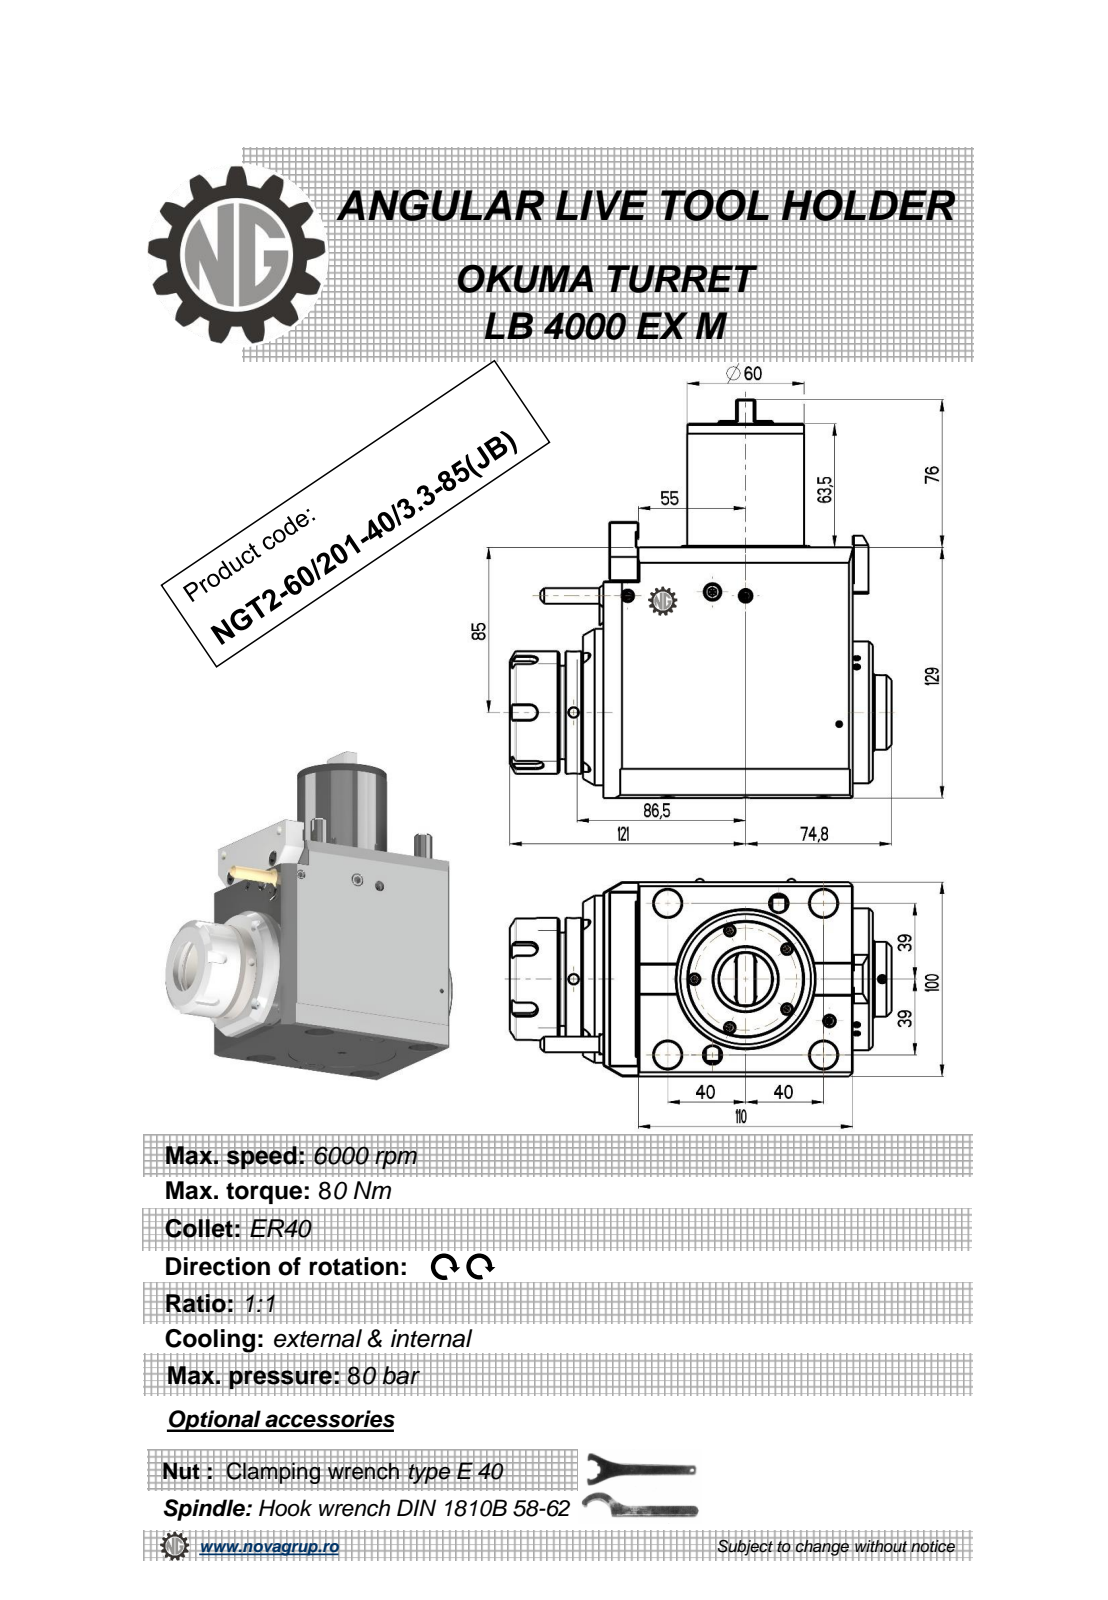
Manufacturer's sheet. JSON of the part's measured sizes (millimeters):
{"part_name": "NGT2_60_201_40_3_3_85_JB", "step_written_by": "PRO/ENGINEER BY PARAMETRIC TECHNOLOGY CORPORATION, 2010280 (CONFIG_CONTROL_DESIGN)", "units": "millimeters", "bodies": {"solids": 2, "faces": 393, "planar": 193, "cylindrical": 91, "other": 109}, "overall_size": [205, 195.8, 100], "volume_mm3": 2054000, "surface_area_mm2": 128659, "round_holes": [[5, 5], [9, 2], [3, 1], [33.5, 1], [71, 1]], "round_bosses_or_shafts": [[12, 4], [6, 3], [86, 1], [73, 1], [63, 1], [60, 1], [51, 1], [38.5, 1]], "partial_cylinders_radius": [[0.31, 10], [0.22, 6], [3.75, 5], [0.8, 2]], "face_to_face_distances": [100, 129, 128, 3, 138.5, 10.5, 0.5, 37.5, 10.3, 138.3], "hole_center_spacings": [42.54, 99.16, 32.19, 68.72, 74, 77.42, 81.23, 85.09]}
